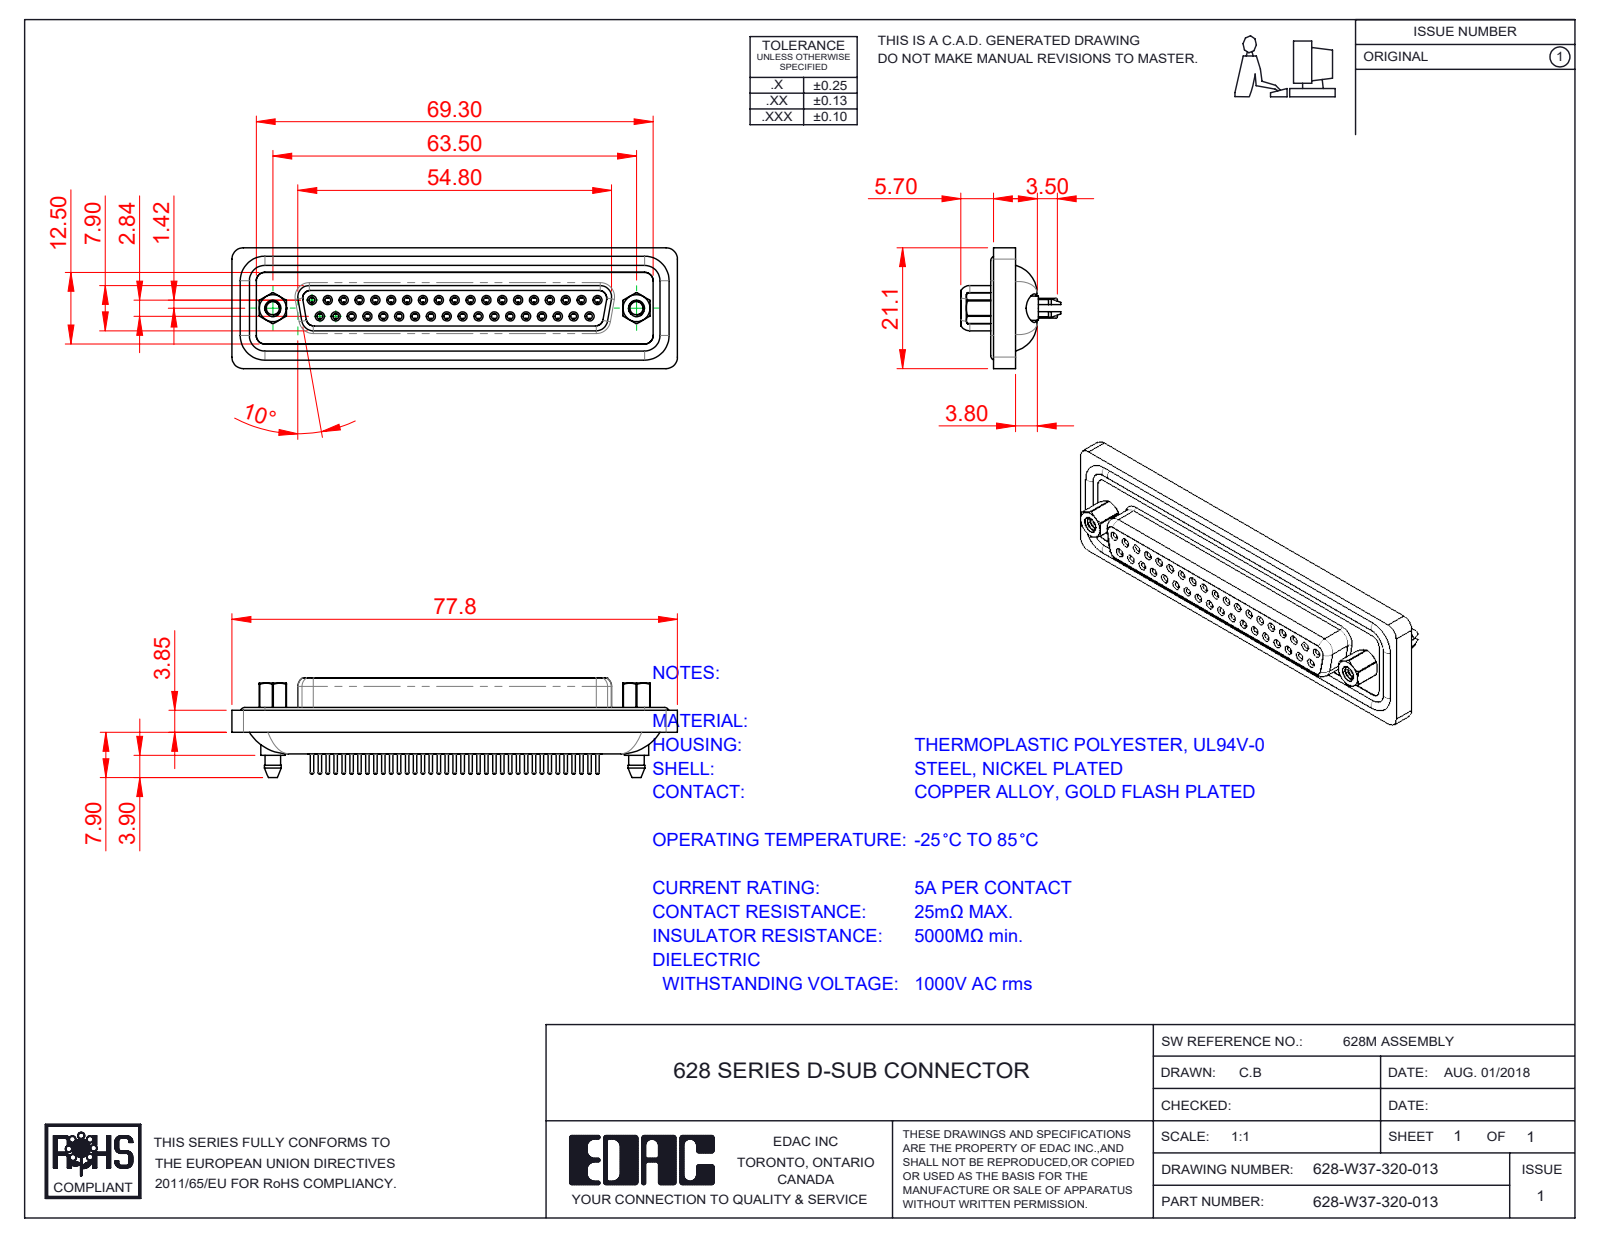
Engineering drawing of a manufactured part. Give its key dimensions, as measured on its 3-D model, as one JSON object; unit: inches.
{"part_name": "628-W37-320-013; 628W 4-40 Hex Standoff; 628W Shell Front_37 Contacts; 628W Housing_37 Contacts (+4 more)", "step_written_by": "SolidWorks 2020 (CONFIG_CONTROL_DESIGN)", "units": "inches", "bodies": {"solids": 45, "faces": 2580, "planar": 670, "cylindrical": 1029, "other": 881}, "overall_size": [3.063, 0.831, 0.687], "volume_in3": 0.673, "surface_area_in2": 28.1, "round_holes": [[0.039, 37], [0.043, 37], [0.059, 37], [0.067, 37], [0.071, 37], [0.079, 37], [0.089, 2], [0.09, 2], [0.157, 2], [0.189, 2], [0.197, 2]], "round_bosses_or_shafts": [[0.063, 41], [0.087, 37], [0.024, 37], [0.059, 8], [0.213, 2], [0.193, 2], [0.167, 2], [0.11, 2]], "partial_cylinders_radius": [[0.059, 16], [0.079, 16], [0.053, 8], [0.063, 6], [0.02, 4], [0.035, 4], [0.069, 4], [0.106, 4]], "face_to_face_distances": [0.016, 0.293, 0.295, 0.333, 0.244, 0.537, 0.148, 0.161, 0.222, 0.043], "hole_center_spacings": [0.124, 0.109, 0.218, 0.327, 0.198, 0.295, 0.436, 0.545]}
